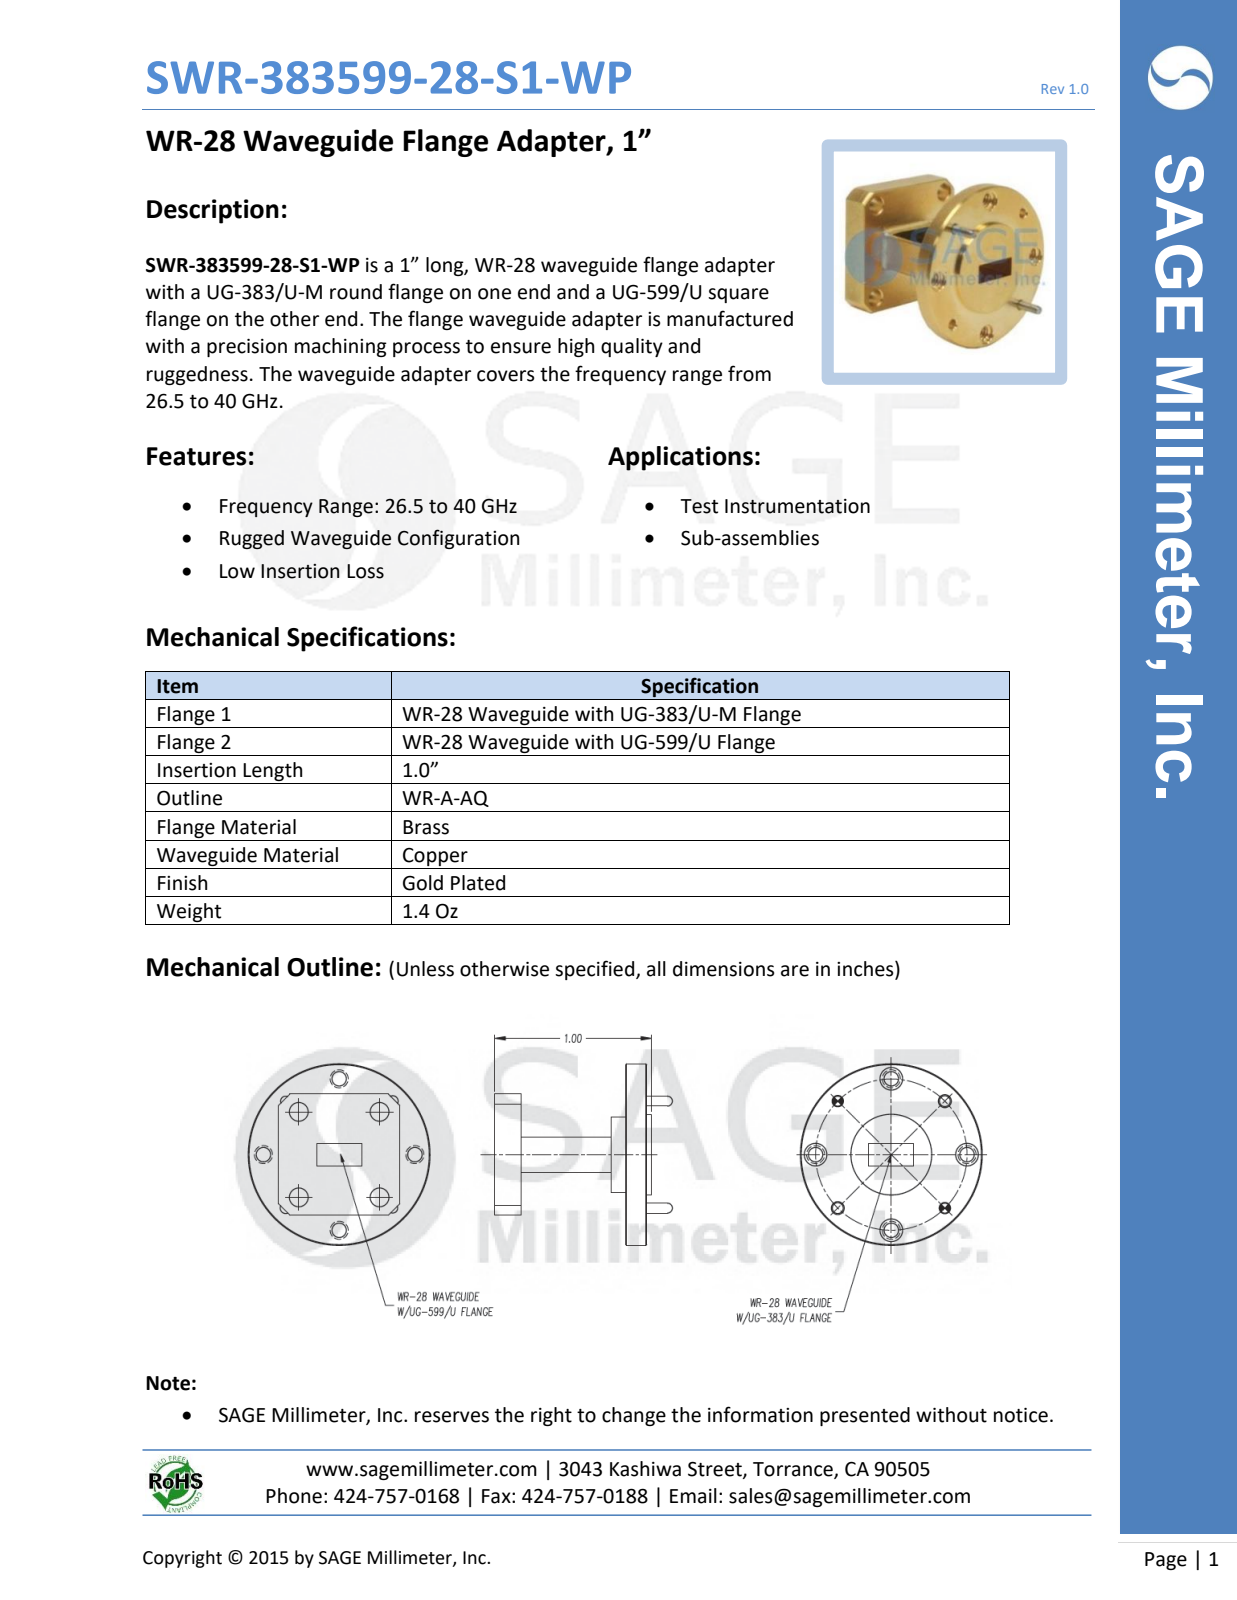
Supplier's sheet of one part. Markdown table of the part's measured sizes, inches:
| quantity | value |
| --- | --- |
| part name | DMWR-28-301-1 |
| STEP written by | SolidWorks 2013 (CONFIG_CONTROL_DESIGN) |
| units | inches |
| bodies | 3 solids, 92 faces (30 planar, 42 cylindrical, 20 other) |
| overall size | 1.125 × 1.125 × 1.123 |
| volume | 0.275 in³ |
| surface area | 6.12 in² |
| round holes (diameter × count) | 0.089 × 4, 0.116 × 4, 0.14 × 4, 0.061 × 2, 0.067 × 2 |
| round bosses / shafts (diameter × count) | 0.063 × 2, 1.125 × 1, 0.5 × 1, 0.47 × 1 |
| main face-to-face distances | 0.16, 0.043, 0.97, 0.81, 0.78, 0.62, 0.19, 0.183, 0.14, 0.322 |
| hole center spacings | 0.359, 0.663, 0.866, 0.105, 0.322, 0.585, 0.602, 0.775 |
